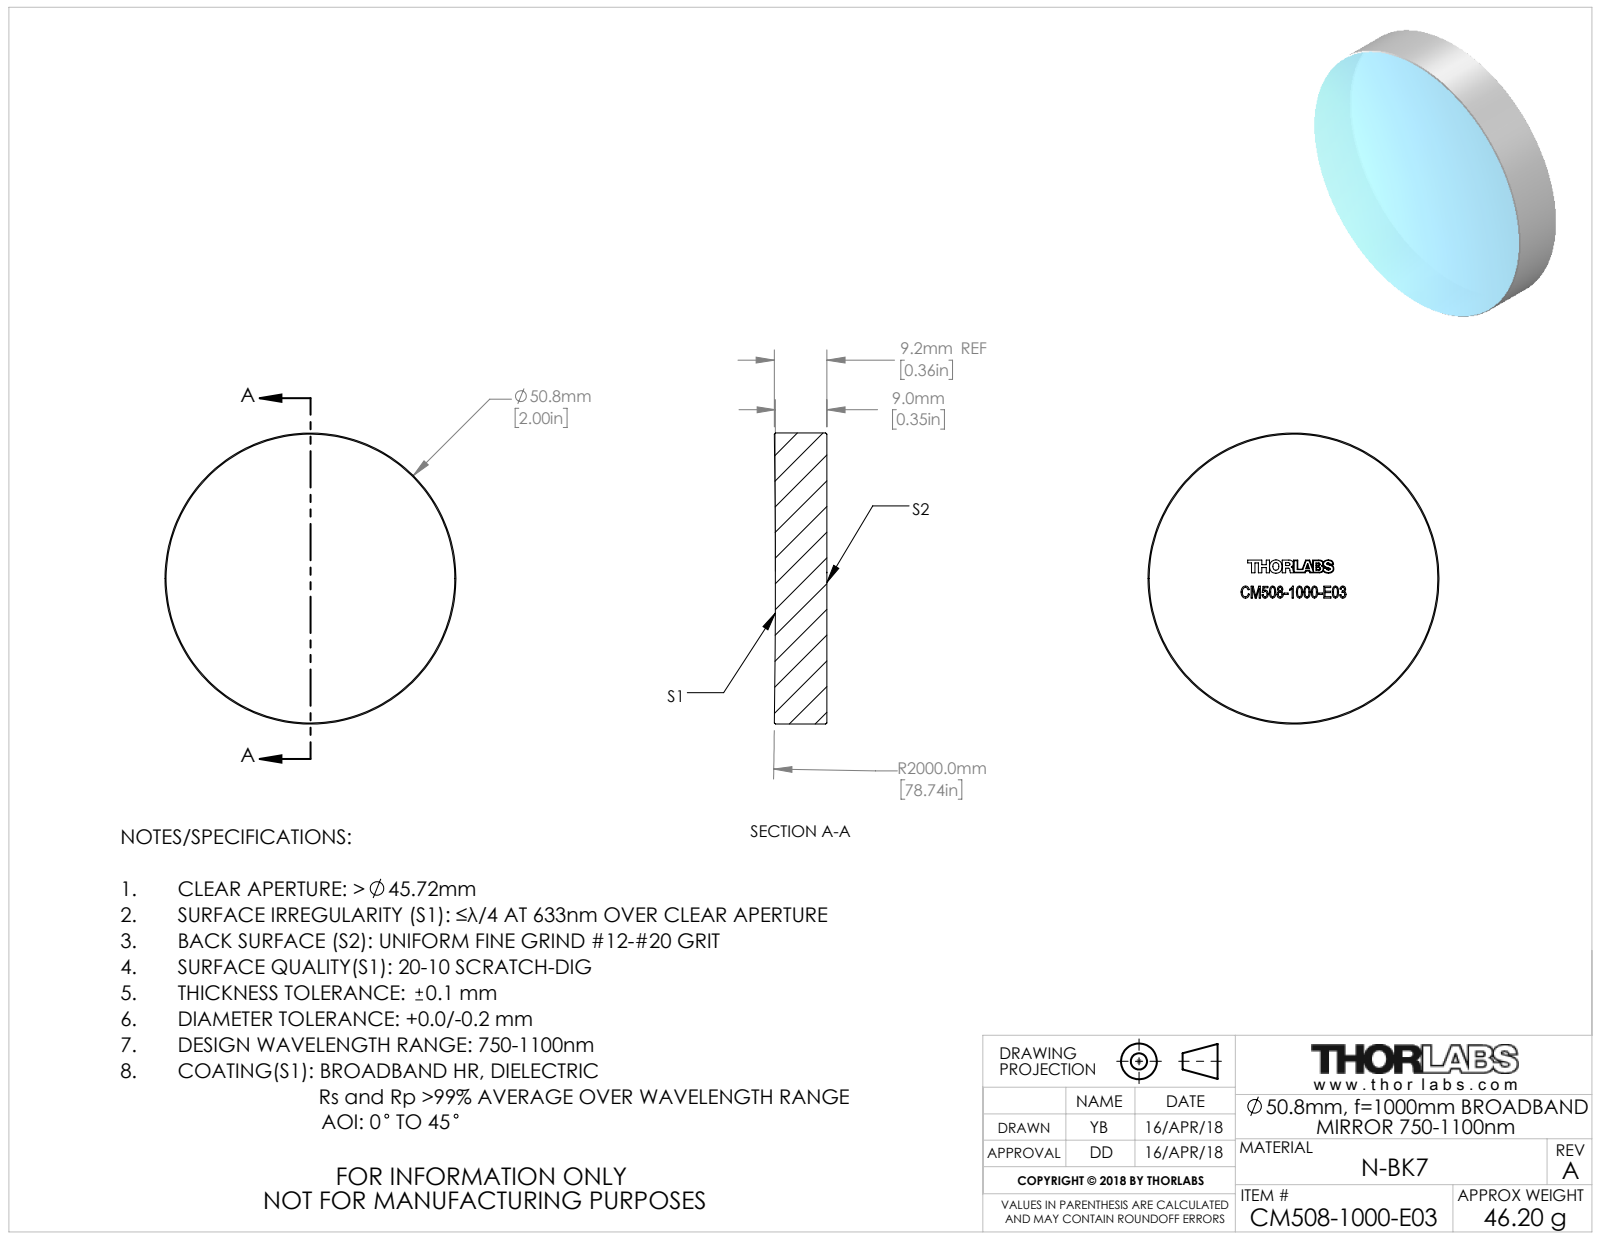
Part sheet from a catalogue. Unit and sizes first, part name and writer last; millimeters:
Units: millimetres
Overall size (bounding box): 50.8 × 50.8 × 9.16
Round bosses / shafts (diameter × count): ⌀50.8 ×1
Volume: 18 399 mm³ · Surface area: 5 478 mm²
Bodies: 1 solid, 45 faces (37 planar, 2 cylindrical, 6 other)
Part name (STEP PRODUCT): TTN153341-E0W
STEP written by: SolidWorks 2018 (CONFIG_CONTROL_DESIGN)
